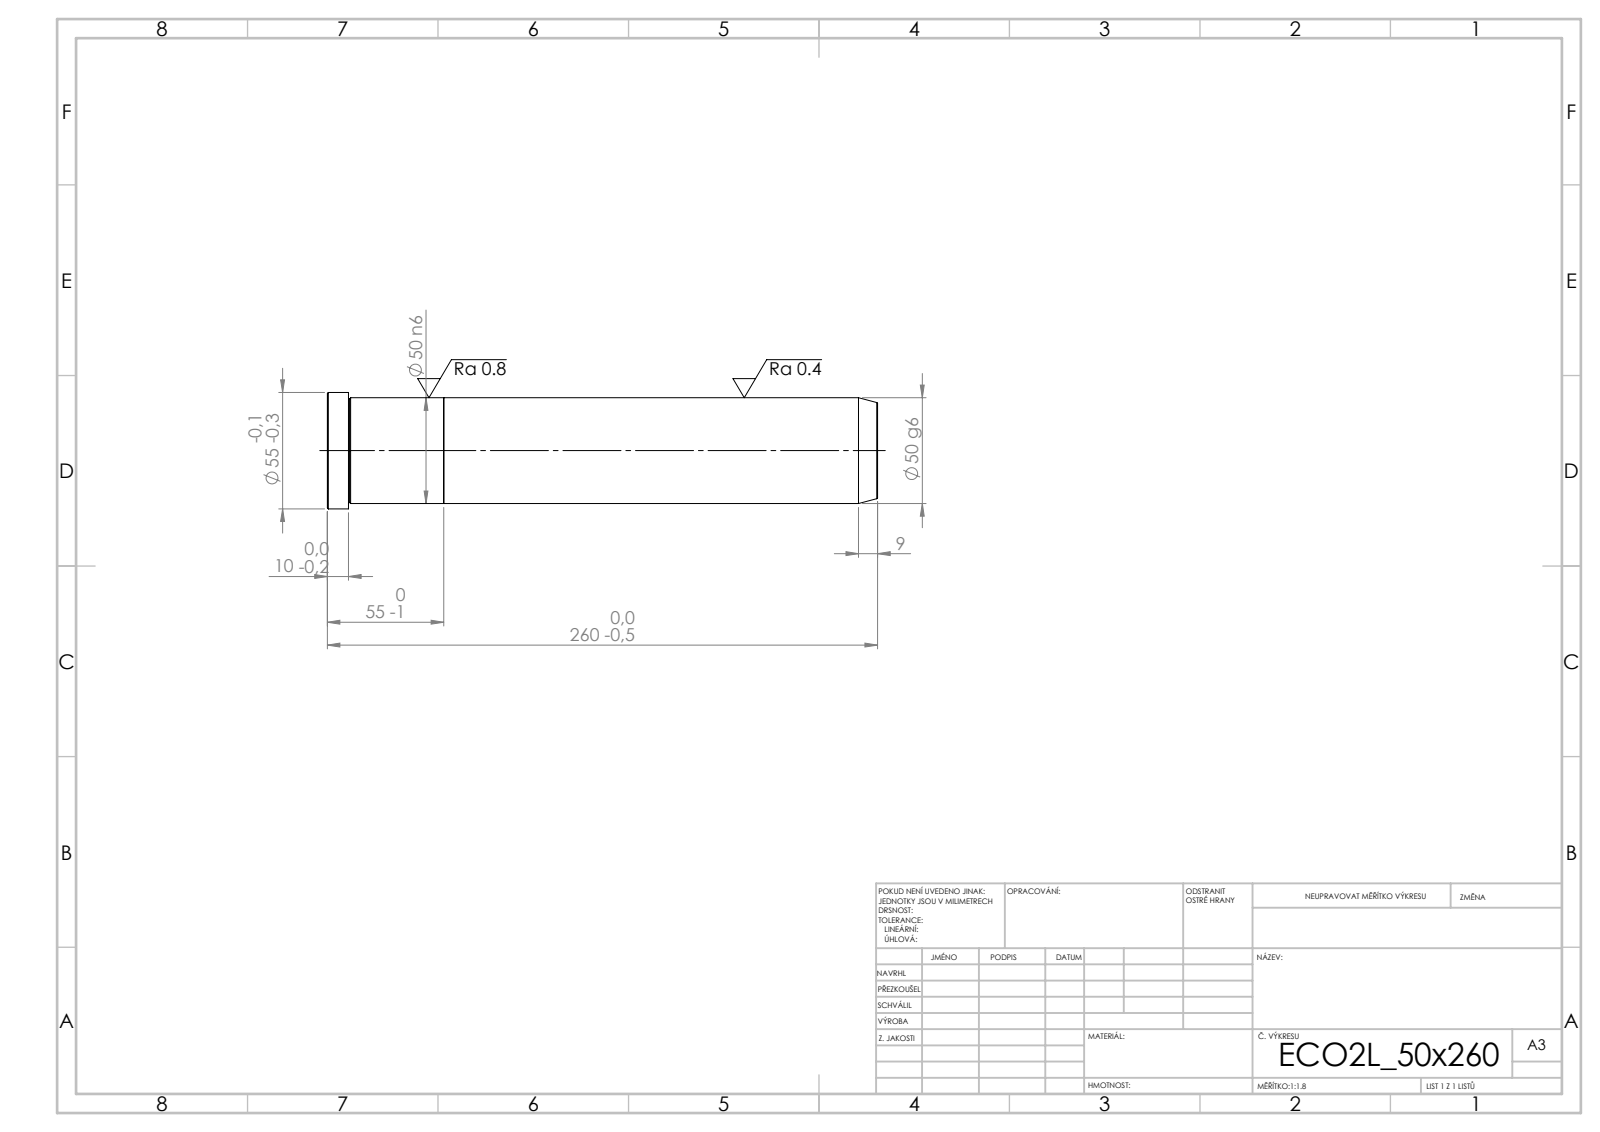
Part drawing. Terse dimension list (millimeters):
written by: SolidWorks 2019 (CONFIG_CONTROL_DESIGN)
unit: mm
bodies: 2 solids, 21 faces (5 planar, 6 cylindrical, 10 other)
size: 260 × 55 × 55
volume: 512 896 mm³; area: 49 315 mm²
bosses: 1× ⌀55, 1× ⌀50
face distances: 55, 205, 260, 250, 45, 10
